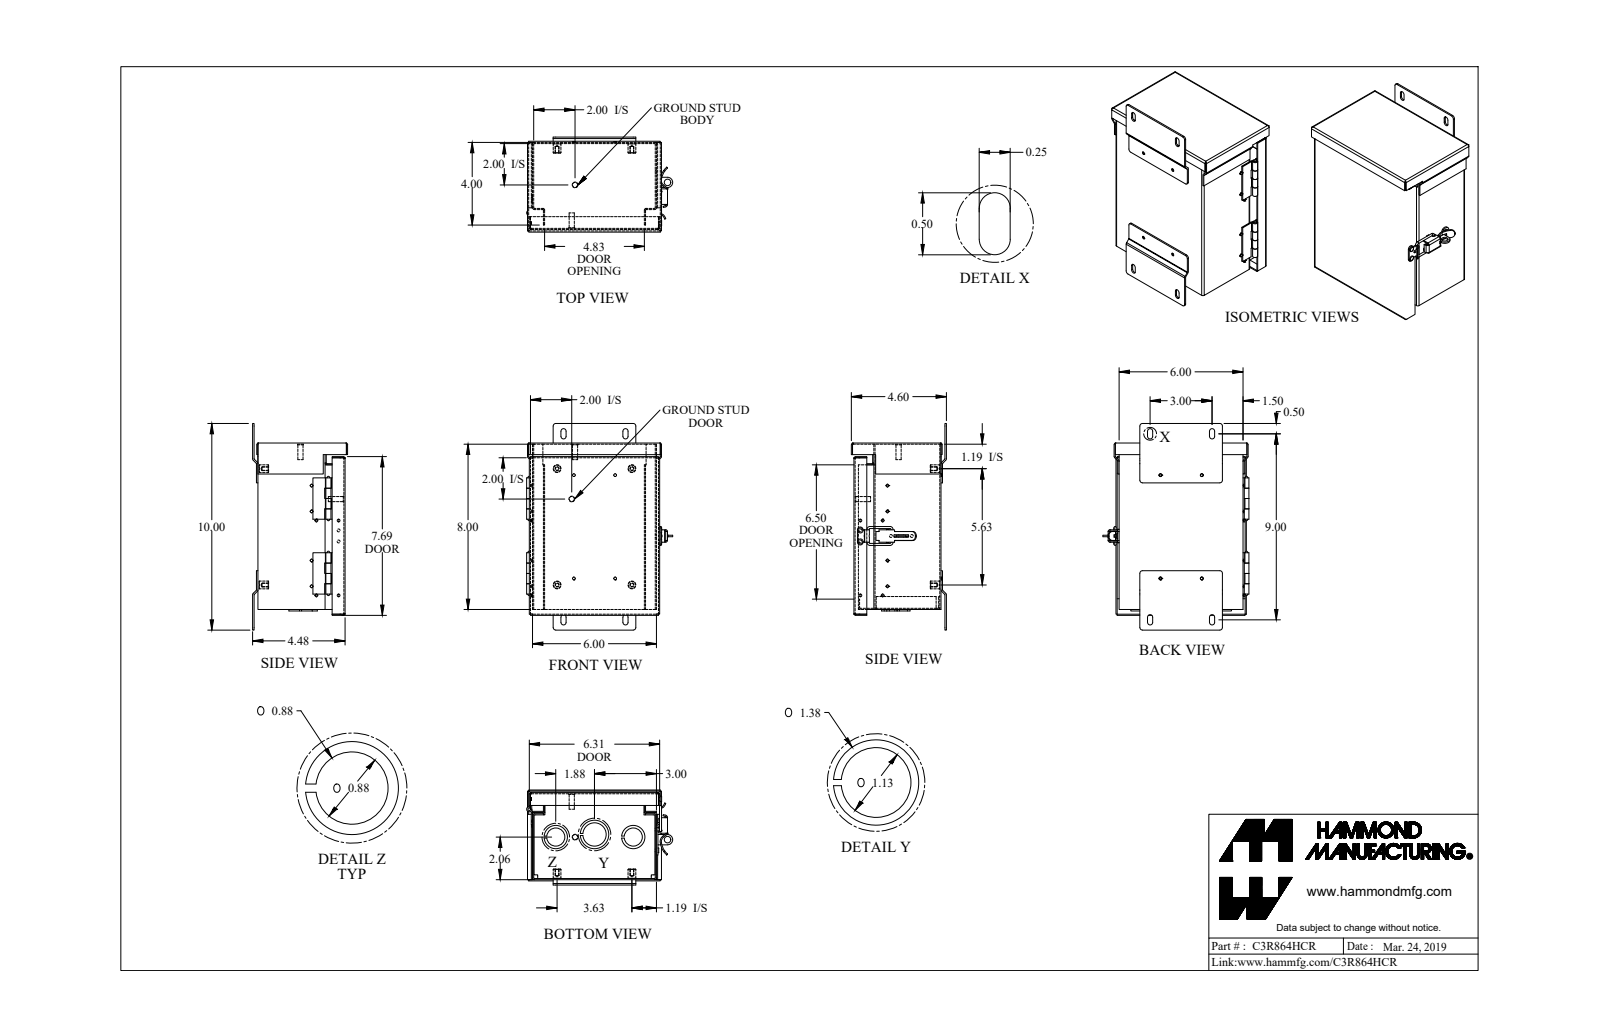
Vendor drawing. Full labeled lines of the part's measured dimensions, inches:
Part name (STEP PRODUCT): C3R864HCR_Default
STEP written by: SolidWorks 2019 (CONFIG_CONTROL_DESIGN)
Units: inches
Bodies: 31 solids, 841 faces (493 planar, 293 cylindrical, 55 other)
Overall size (bounding box): 10 × 7.07 × 4.599
Volume: 21.55 in³ · Surface area: 677.9 in²
Round holes (diameter × count): ⌀0.137 ×4, ⌀0.14 ×4, ⌀0.156 ×4, ⌀0.133 ×2, ⌀0.145 ×2, ⌀0.875 ×2, ⌀0.125 ×1, ⌀0.13 ×1, ⌀0.313 ×1, ⌀1.125 ×1
Round bosses / shafts (diameter × count): ⌀0.131 ×12, ⌀0.375 ×4, ⌀0.125 ×4, ⌀0.1 ×4, ⌀1.125 ×2, ⌀0.281 ×2, ⌀0.25 ×2, ⌀1.375 ×1
Partial cylindrical surfaces — rounded edges, fillets, slot ends (radius × count): R0.029 ×28, R0.086 ×28, R0.125 ×22, R0.036 ×6, R0.108 ×6, R0.135 ×2, R0.04 ×1, R0.067 ×1
Main face-to-face distances: 0.057, 4.16, 4.103, 5.943, 4.217, 0.187, 8, 0.244, 6, 7.943
Hole centre spacings: 1.498, 1.01, 1.01, 2, 2.498, 2.829, 2.83, 3.625
